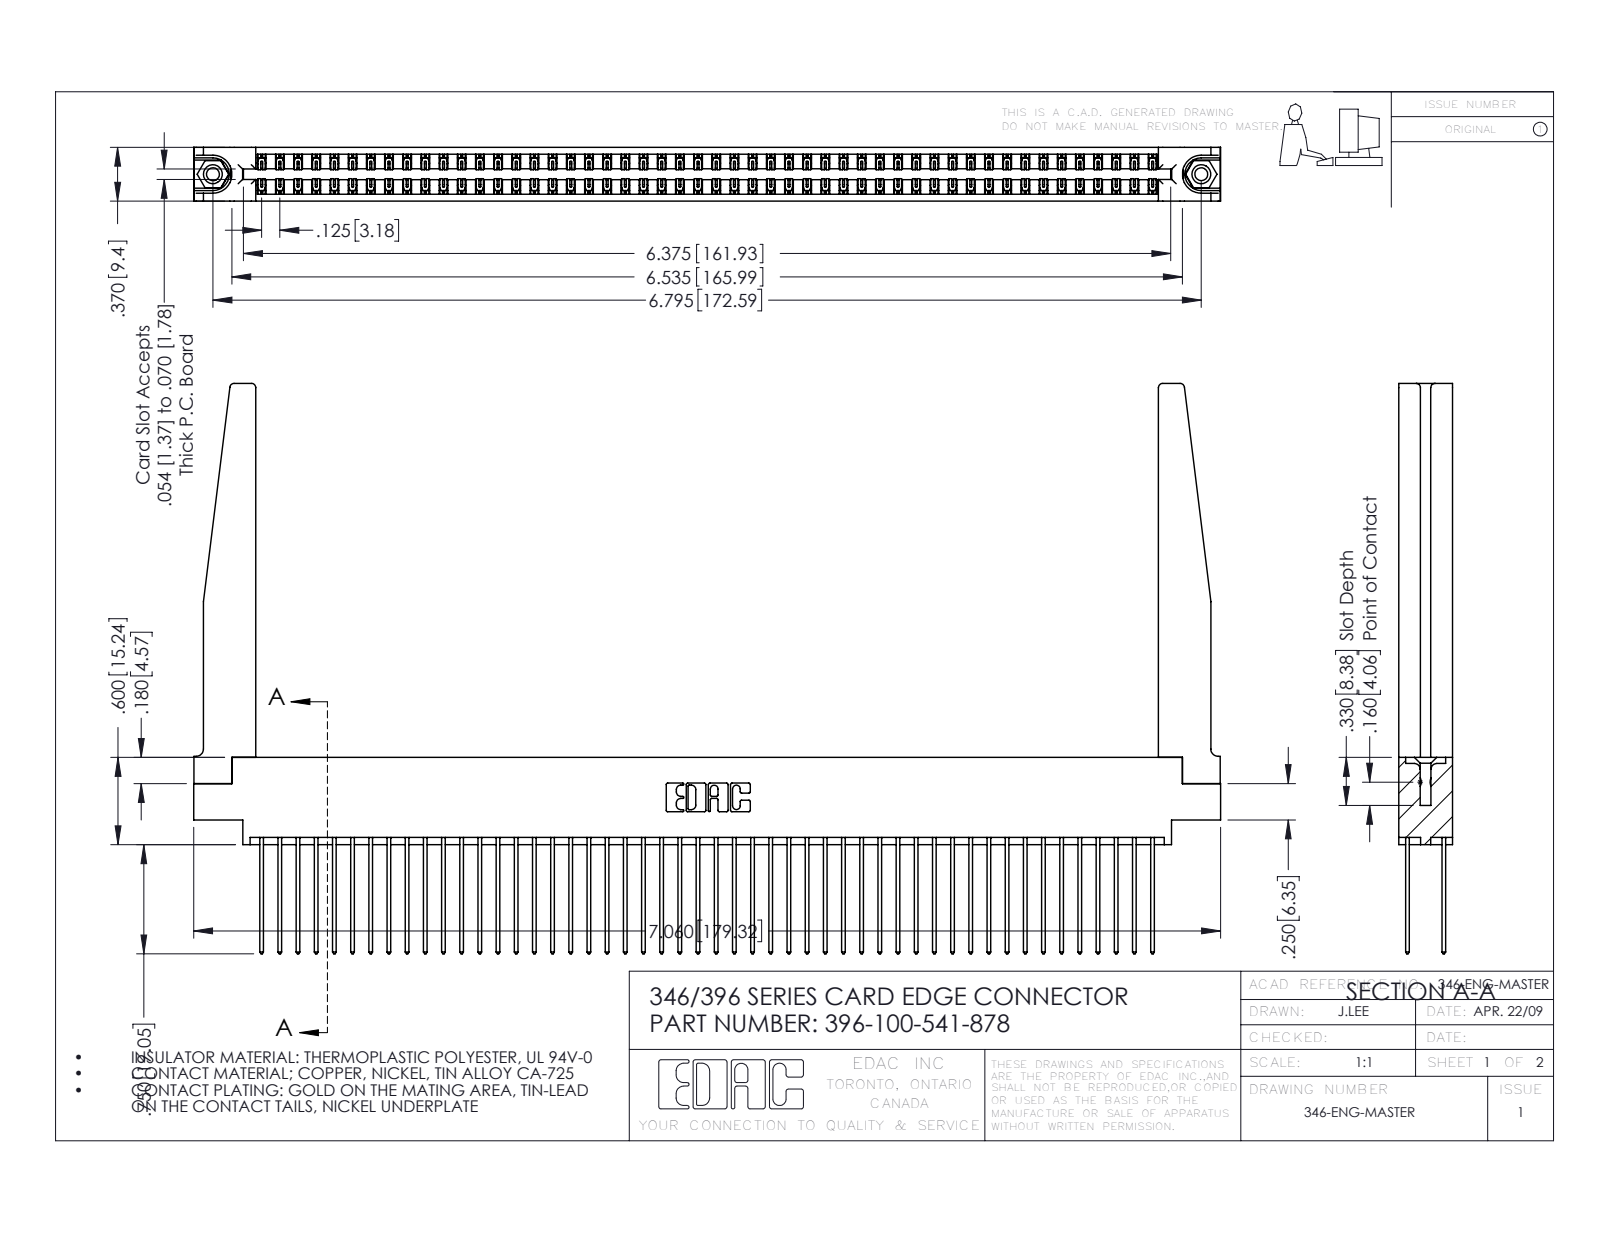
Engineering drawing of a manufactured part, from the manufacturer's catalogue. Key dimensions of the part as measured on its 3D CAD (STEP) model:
Part name (STEP PRODUCT): 346-220-078_345-220-078; 345-292-001_345-293-141; 345-250-001_345-250-001-102; 396-100-541-878 (+1 more)
STEP written by: SolidWorks 2016 (CONFIG_CONTROL_DESIGN)
Units: inches
Bodies: 105 solids, 5560 faces (3722 planar, 1786 cylindrical, 52 other)
Overall size (bounding box): 7.06 × 3.92 × 0.37
Volume: 1.518 in³ · Surface area: 53.15 in²
Round holes (diameter × count): ⌀0.089 ×2, ⌀0.125 ×2, ⌀0.156 ×2, ⌀0.064 ×1
Round bosses / shafts (diameter × count): ⌀0.155 ×2
Partial cylindrical surfaces — rounded edges, fillets, slot ends (radius × count): R0.006 ×150, R0.01 ×100, R0.01 ×22, R0.03 ×8, R0.007 ×6, R0.031 ×6, R0.026 ×3, R0.014 ×2
Main face-to-face distances: 0.048, 0.322, 0.37, 0.072, 0.25, 0.298, 0.025, 0.275, 0.148, 0.15
Hole centre spacings: 0.246, 6.586, 6.795
